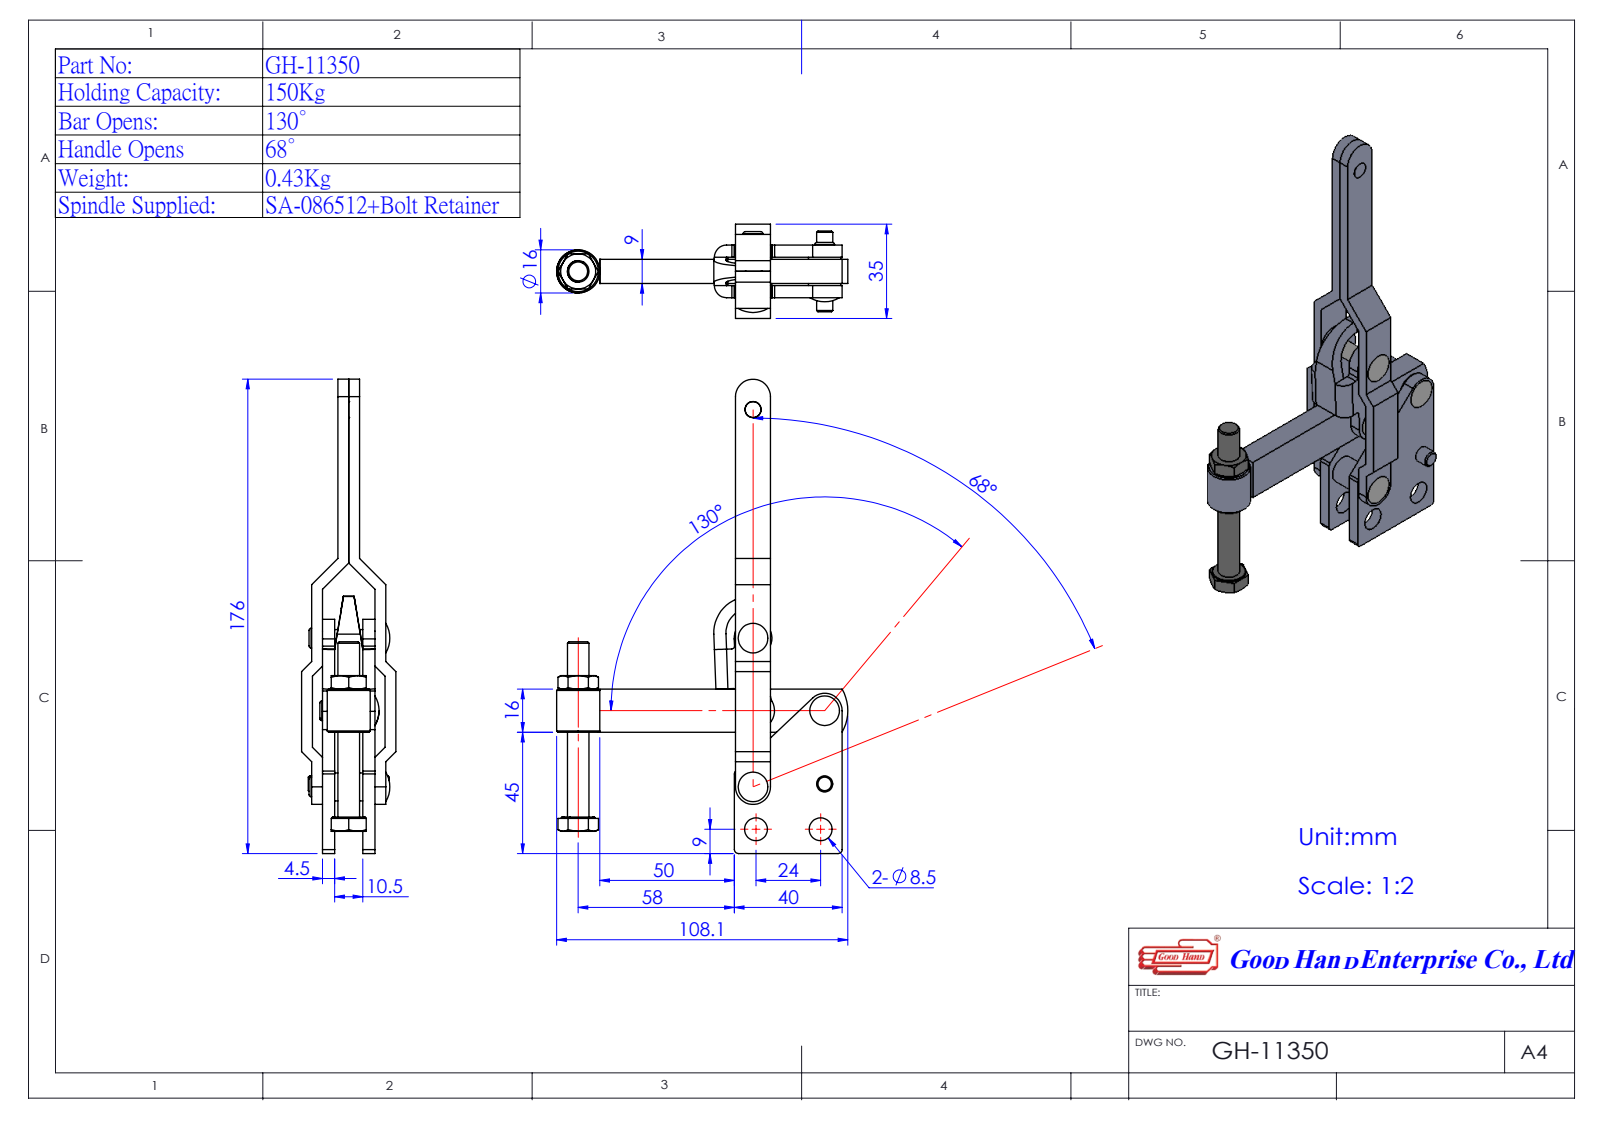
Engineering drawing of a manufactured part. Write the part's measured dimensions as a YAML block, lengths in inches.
part_name: "Group1^GH-11350(簡化); 13508-1^GH-11350(簡化); Group4^GH-11350(簡化); Group2^GH-11350(簡化) (+2 more)"
step_written_by: "SolidWorks 2016 (AUTOMOTIVE_DESIGN)"
units: inches
bodies: {solids: 5, faces: 212, planar: 92, cylindrical: 79, other: 41}
overall_size: [6.929, 4.256, 1.378]
volume: 3.713
surface_area: 51.86
round_holes:
  - {diameter: 0.177, count: 4}
  - {diameter: 0.335, count: 2}
round_bosses_or_shafts:
  - {diameter: 0.287, count: 4}
  - {diameter: 0.315, count: 2}
  - {diameter: 0.63, count: 1}
  - {diameter: 0.492, count: 1}
  - {diameter: 0.236, count: 1}
partial_cylinders:
  - {radius: 0.059, count: 3}
  - {radius: 0.256, count: 3}
  - {radius: 0.039, count: 2}
  - {radius: 0.157, count: 2}
  - {radius: 0.177, count: 2}
  - {radius: 0.276, count: 2}
  - {radius: 0.63, count: 1}
face_to_face_distances: [0.177, 0.384, 0.207, 0.591, 0.157, 0.561, 0.03, 0.768, 0.335, 0.364]
hole_center_spacings: [0.621, 0.945, 1.008, 1.061, 1.114, 1.166, 1.49, 1.528]
